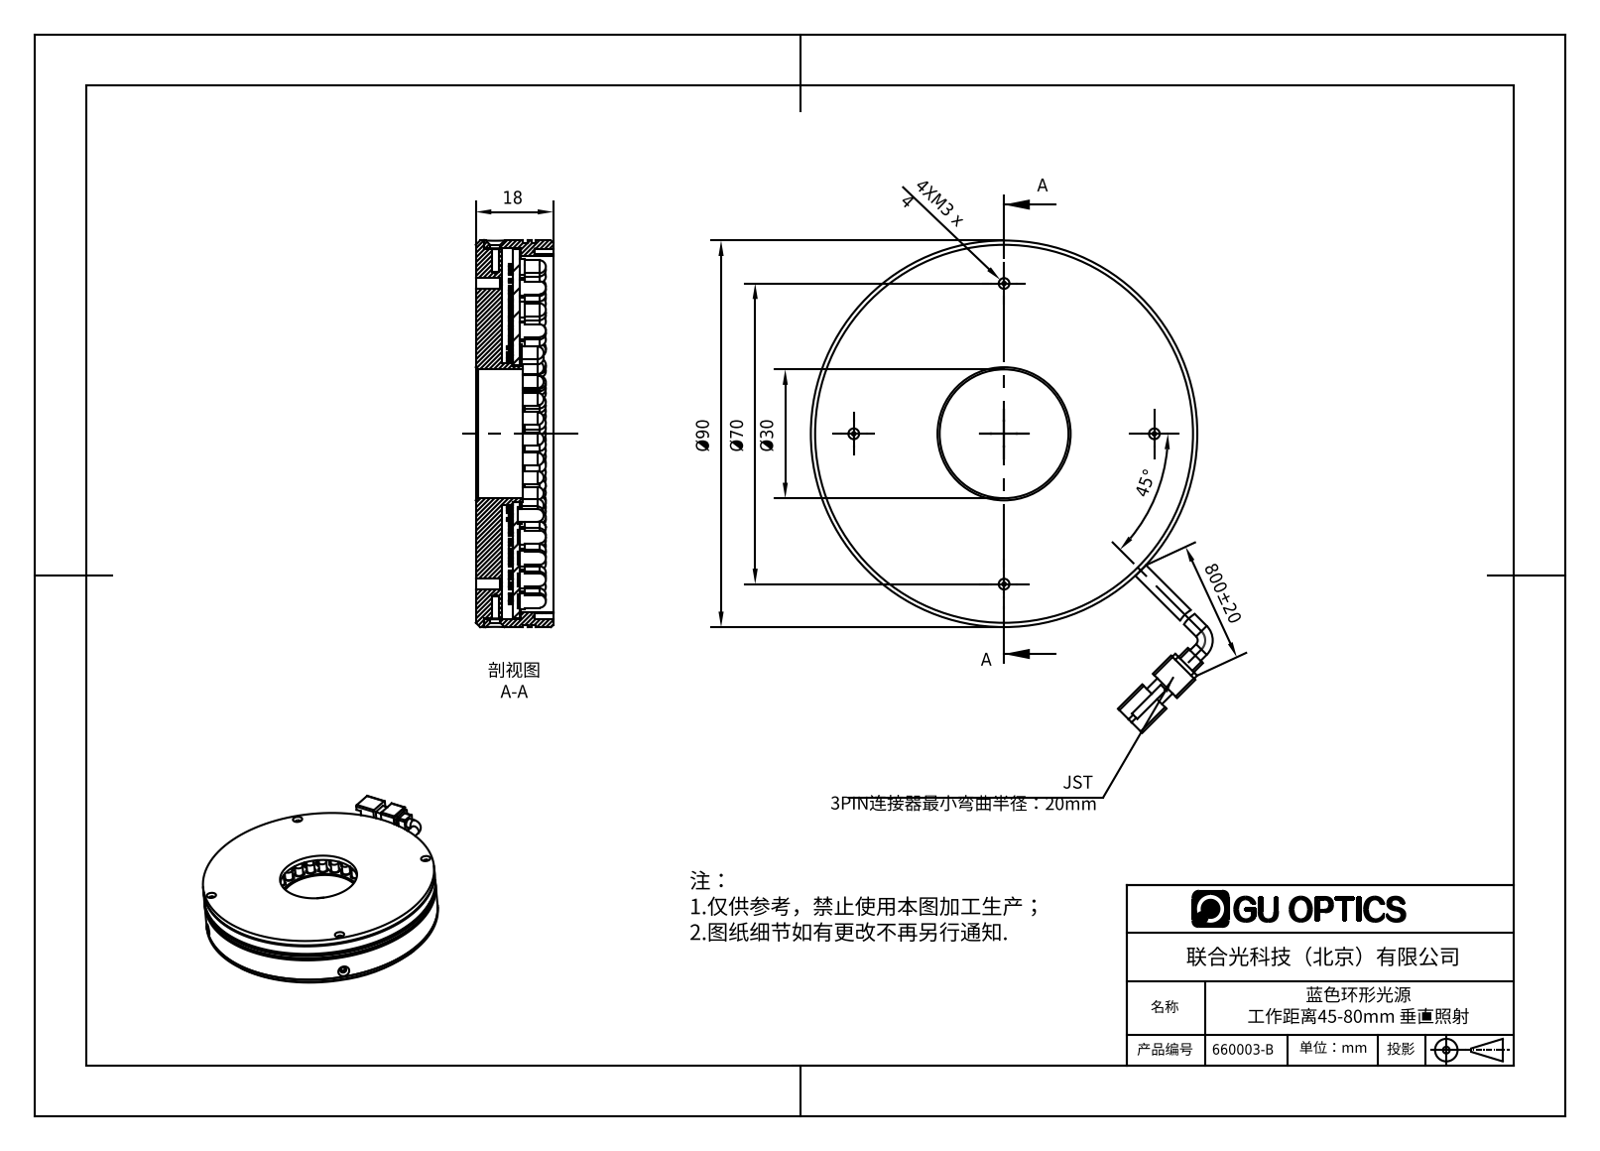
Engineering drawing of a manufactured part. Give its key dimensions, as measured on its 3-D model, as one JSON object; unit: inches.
{"part_name": "660003-B", "step_written_by": "SolidWorks 2016 (AUTOMOTIVE_DESIGN)", "units": "inches", "bodies": {"solids": 181, "faces": 3232, "planar": 2184, "cylindrical": 822, "other": 226}, "overall_size": [4.514, 3.685, 0.884], "volume_in3": 4.328, "surface_area_in2": 100.2, "round_holes": [[0.122, 5], [0.049, 4], [0.067, 4], [0.098, 4], [0.063, 2], [0.094, 2], [1.181, 1], [1.26, 1], [3.268, 1], [3.402, 1]], "round_bosses_or_shafts": [[0.15, 175], [0.118, 175], [0.138, 2], [3.543, 1], [3.504, 1], [3.386, 1], [1.299, 1], [1.244, 1]], "partial_cylinders_radius": [[0.02, 12], [0.039, 4], [0.065, 1], [0.236, 1]], "face_to_face_distances": [0.079, 0.303, 0.709, 0.343, 0.445, 0.366, 0.382, 0.236, 0.406, 0.787], "hole_center_spacings": [2.168, 0.197, 0.295, 1.378, 1.673, 1.949, 2.366, 3.051]}
